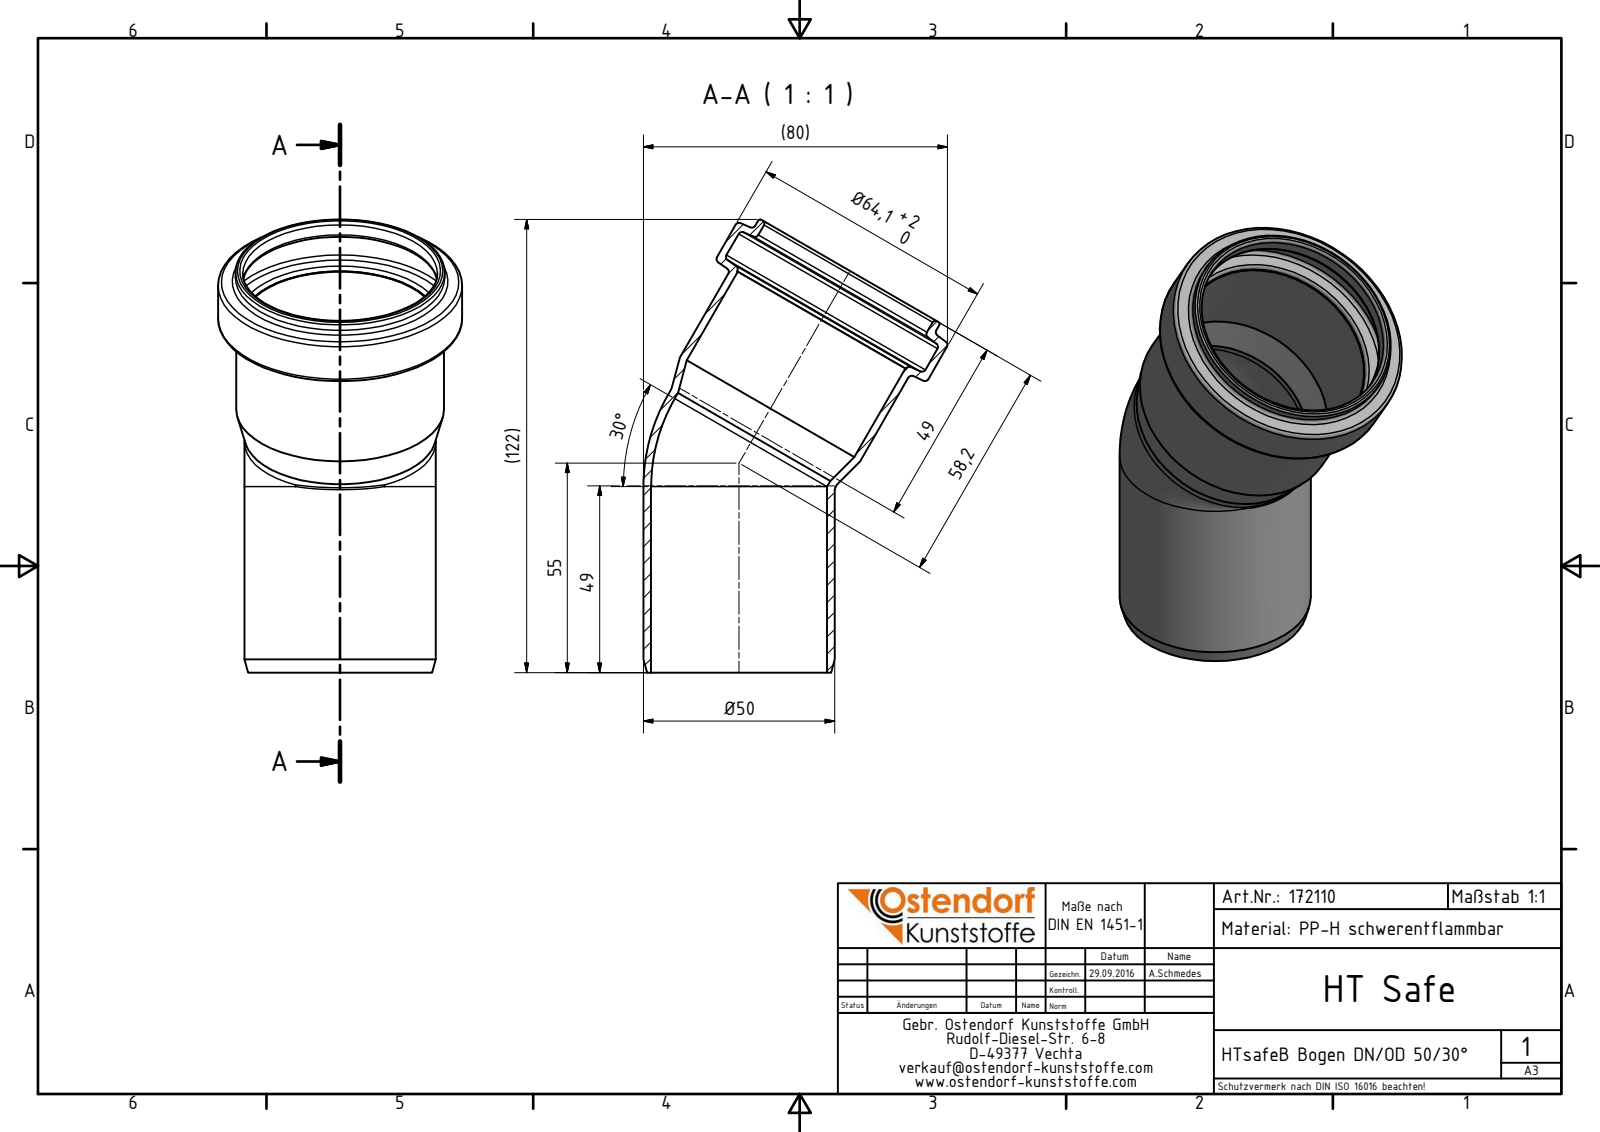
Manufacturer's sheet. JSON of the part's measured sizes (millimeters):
{"part_name": "172110 HTsafeB DN_OD 50_30°", "step_written_by": "Autodesk Inventor 2016 (AUTOMOTIVE_DESIGN)", "units": "millimeters", "bodies": {"solids": 1, "faces": 34, "planar": 3, "cylindrical": 11, "other": 20}, "overall_size": [118.94, 79.85, 64.1], "volume_mm3": 37599, "surface_area_mm2": 39182, "round_holes": [[46.2, 2], [50.8, 1], [51.1, 1], [60.3, 1]], "round_bosses_or_shafts": [[50.2, 2], [64.1, 1], [54.9, 1], [54.6, 1]], "face_to_face_distances": [14.9]}
